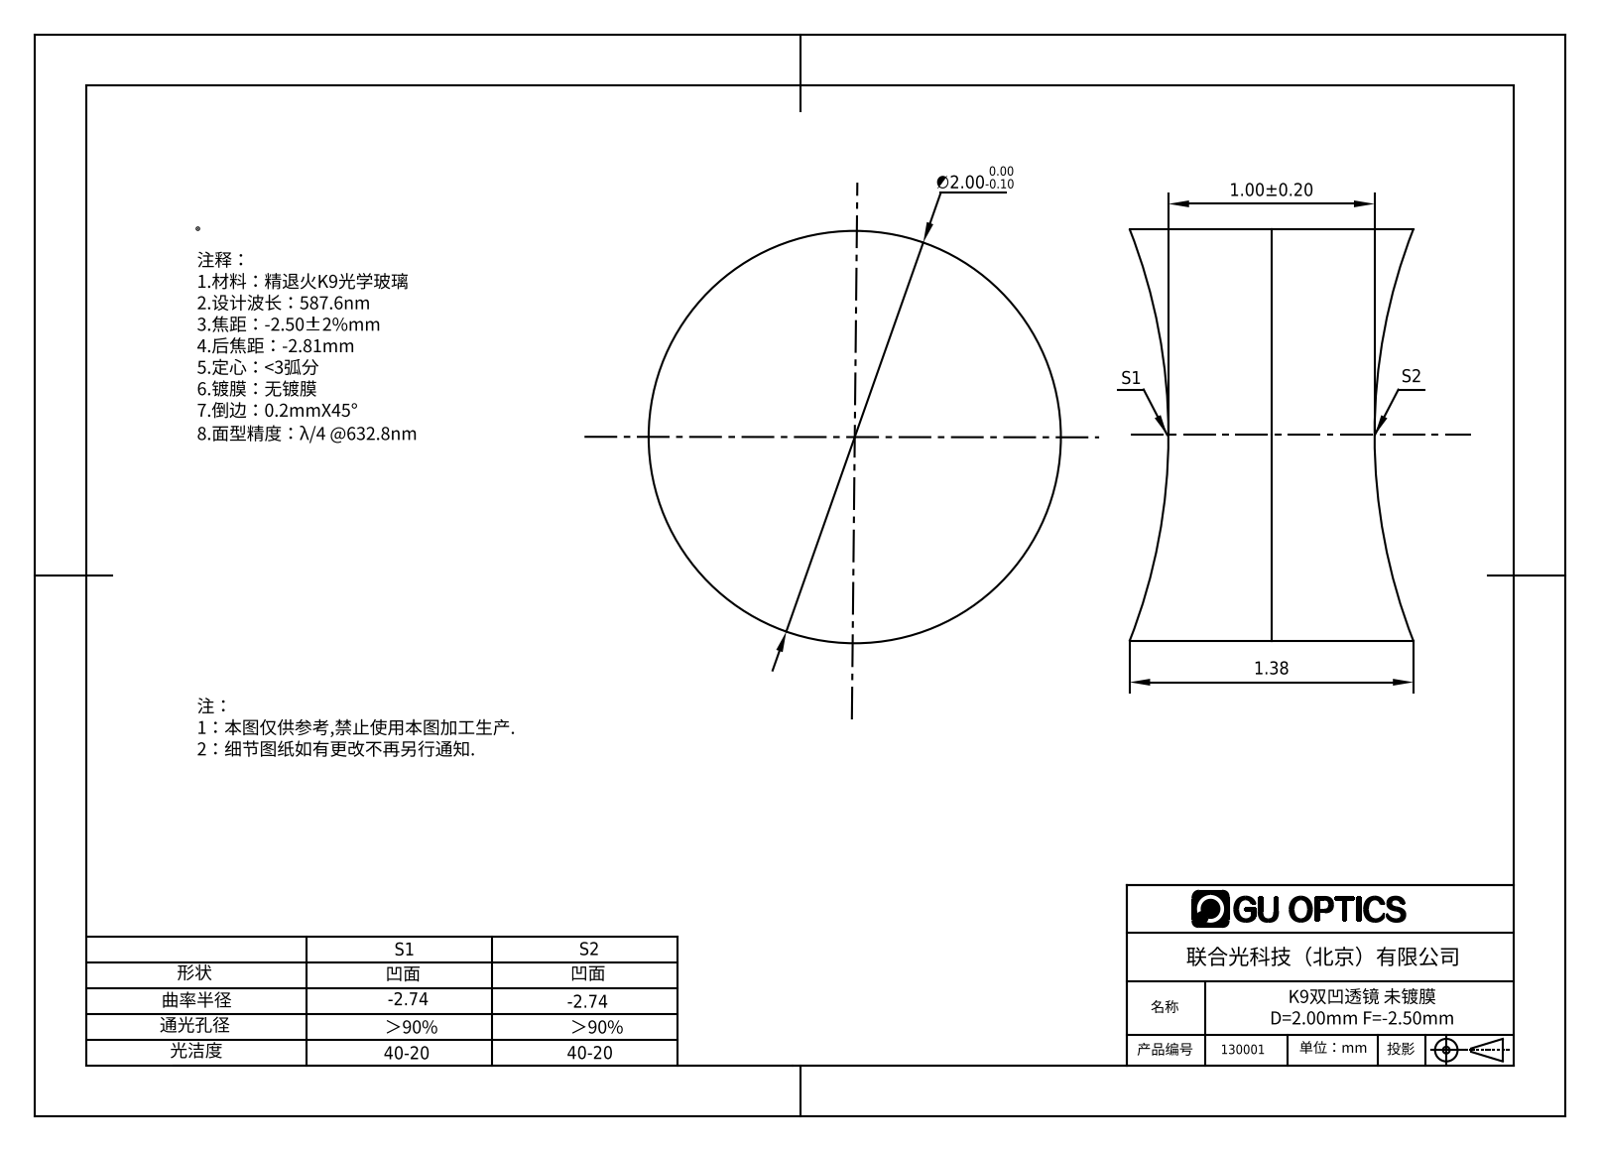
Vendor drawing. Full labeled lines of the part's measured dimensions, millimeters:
Part name (STEP PRODUCT): 130001
STEP written by: SolidWorks 2016 (AUTOMOTIVE_DESIGN)
Units: millimetres
Bodies: 1 solid, 6 faces (0 planar, 2 cylindrical, 4 other)
Overall size (bounding box): 2 × 2 × 1.38
Volume: 4 mm³ · Surface area: 15 mm²
Round bosses / shafts (diameter × count): ⌀2 ×1
